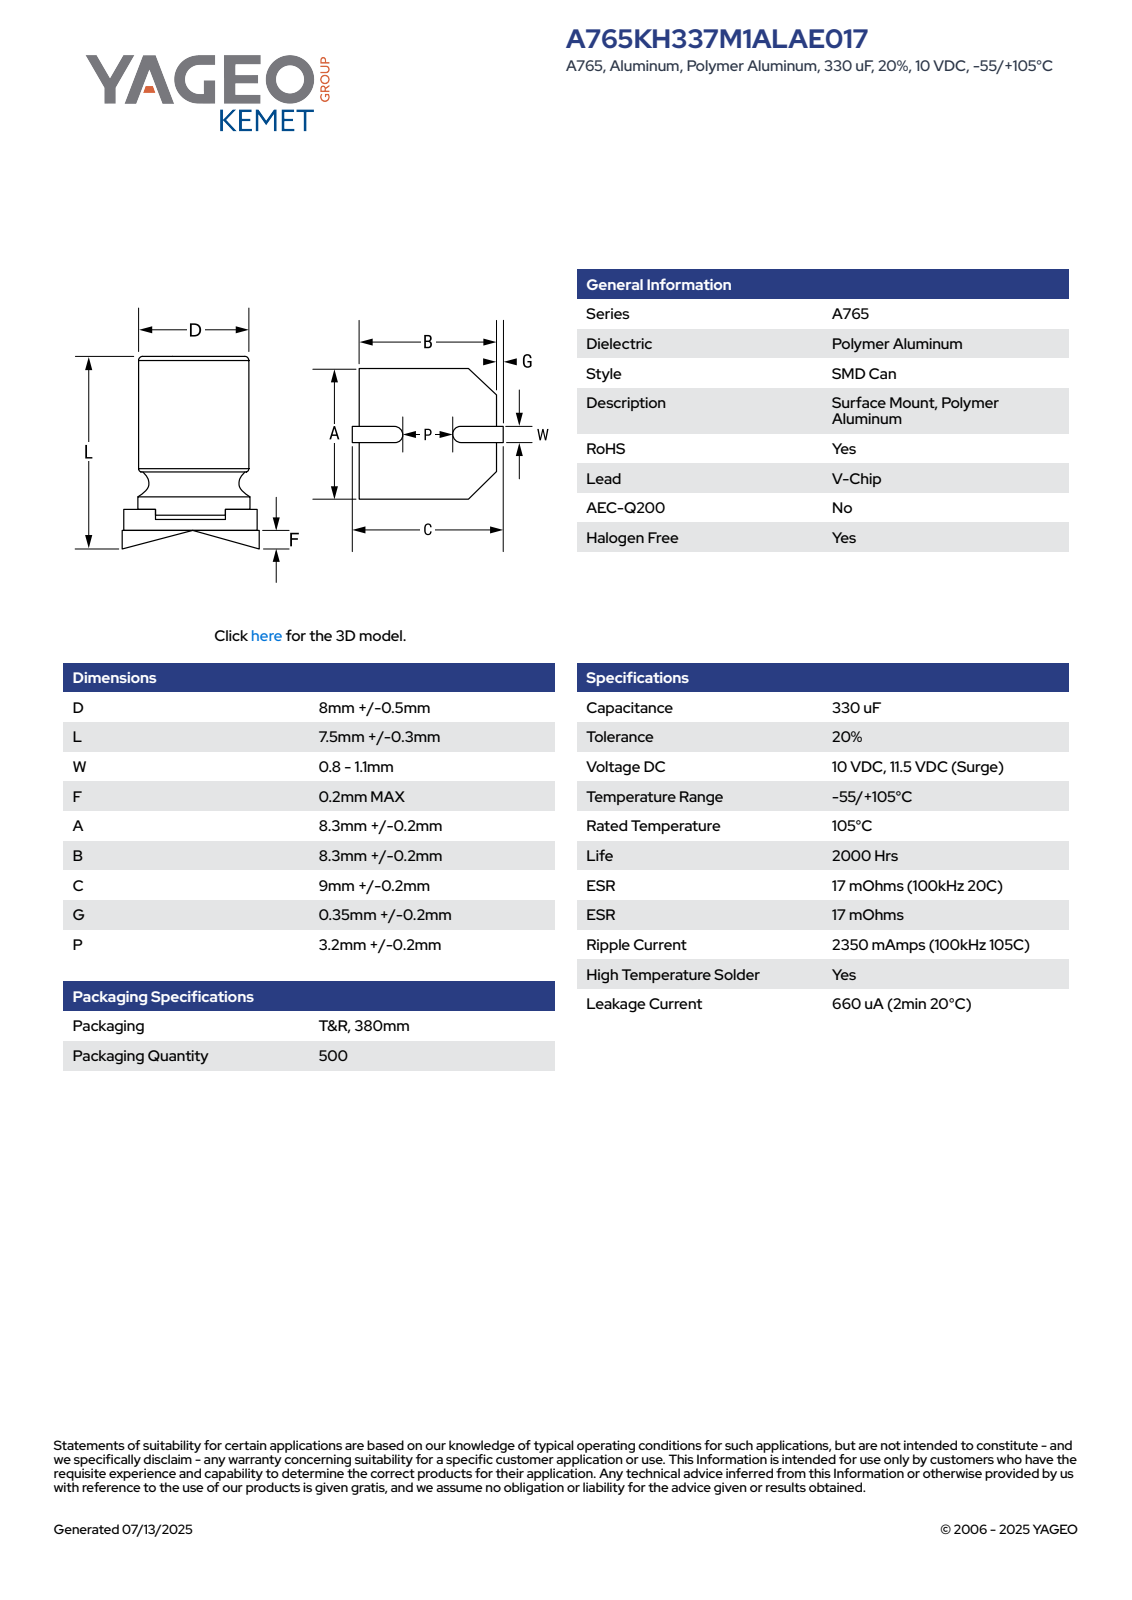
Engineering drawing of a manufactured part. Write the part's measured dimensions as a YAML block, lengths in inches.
part_name: "CAC_KS_8X7.5_D8.5L7.8W1.1F0.2A8.5B8.5C9.2P3.4"
step_written_by: "SolidWorks 2014 (AUTOMOTIVE_DESIGN)"
units: inches
bodies: {solids: 5, faces: 76, planar: 59, cylindrical: 11, other: 6}
overall_size: [0.362, 0.335, 0.307]
volume: 0.025
surface_area: 0.767
round_bosses_or_shafts:
  - {diameter: 0.32, count: 1}
partial_cylinders:
  - {radius: 0.008, count: 2}
  - {radius: 0.133, count: 1}
  - {radius: 0.167, count: 1}
face_to_face_distances: [0.015, 0.299, 0.284, 0.335, 0.077, 0.061, 0.222, 0.023, 0.085, 0.307]
